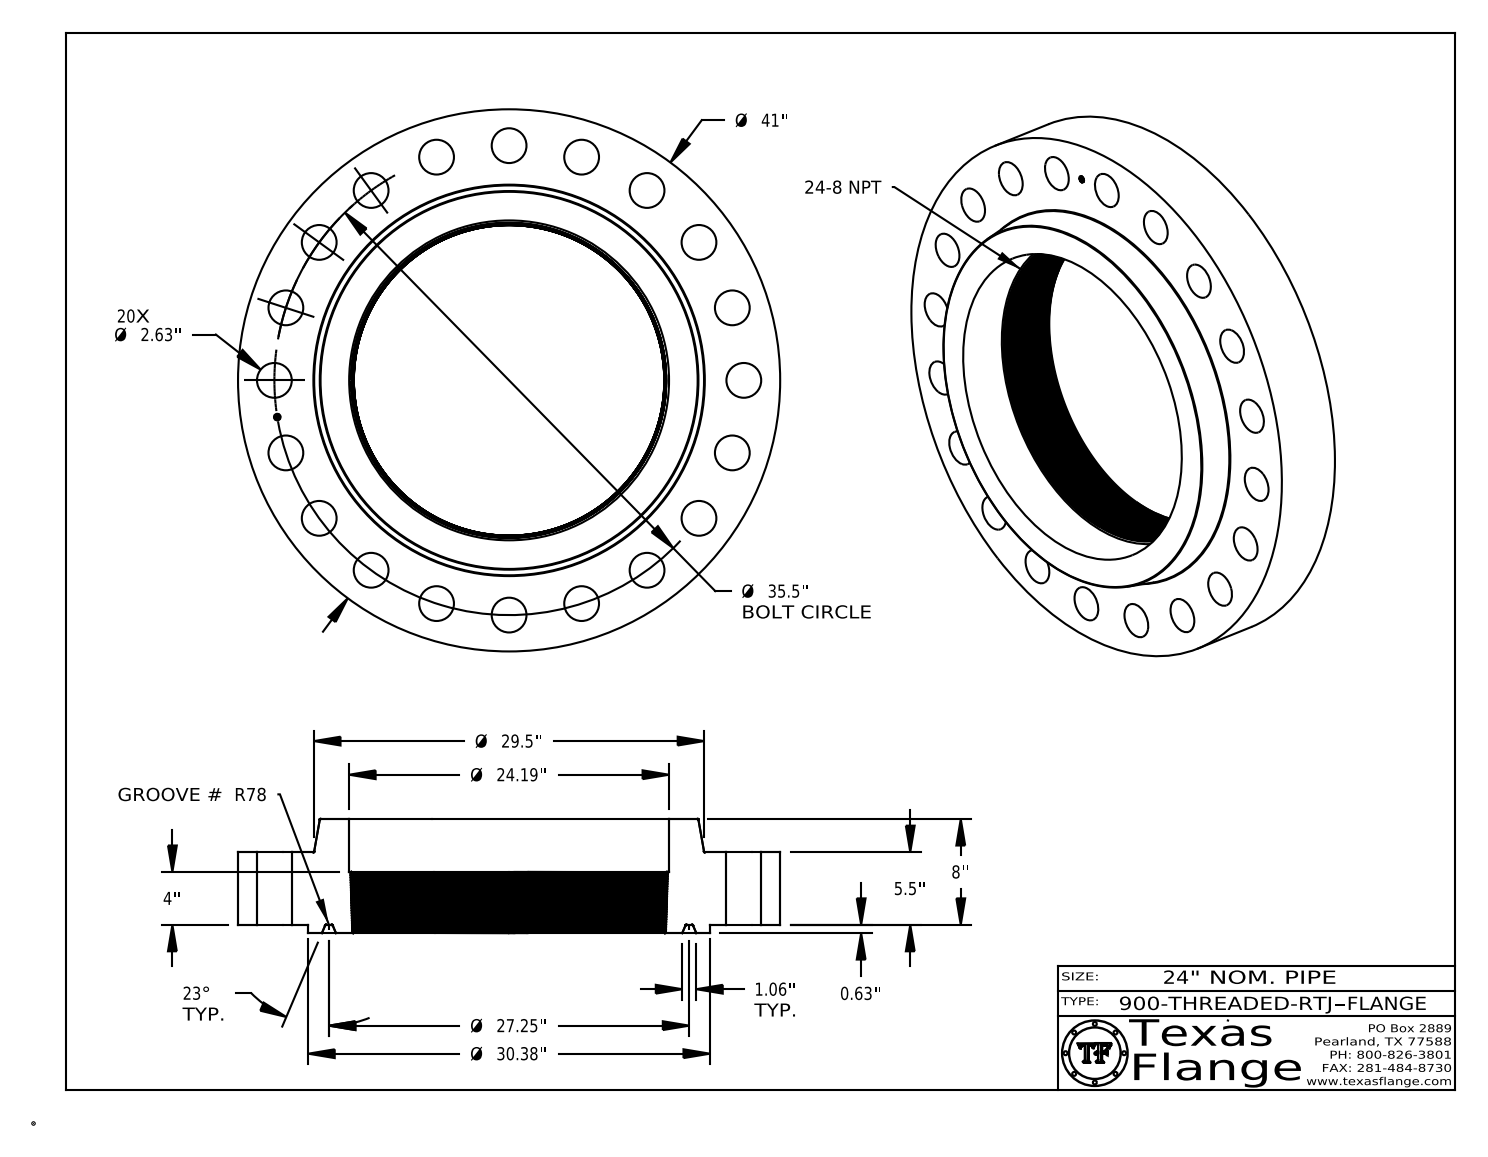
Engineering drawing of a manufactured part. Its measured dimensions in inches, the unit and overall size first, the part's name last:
Units: inches
Overall size (bounding box): 41 × 41 × 8.625
Round holes (diameter × count): ⌀2.63 ×20, ⌀0.495 ×1, ⌀24.19 ×1
Round bosses / shafts (diameter × count): ⌀0.03 ×8, ⌀41 ×1, ⌀30.375 ×1, ⌀0.39 ×1
Main face-to-face distances: 5.5, 0.625, 6.125, 8.625, 8, 2.5, 4, 4.625, 1.5, 6.11
Hole centre spacings: 17.75, 10.97, 28.72, 31.631, 16.117, 20.866, 25.102, 33.762
Volume: 4 851 in³ · Surface area: 4 424 in²
Bodies: 1 solid, 829 faces (372 planar, 66 cylindrical, 391 other)
Part name (STEP PRODUCT): 900-THREADED-RTJ
STEP written by: CATIA V5 STEP AP214 (AUTOMOTIVE_DESIGN)
